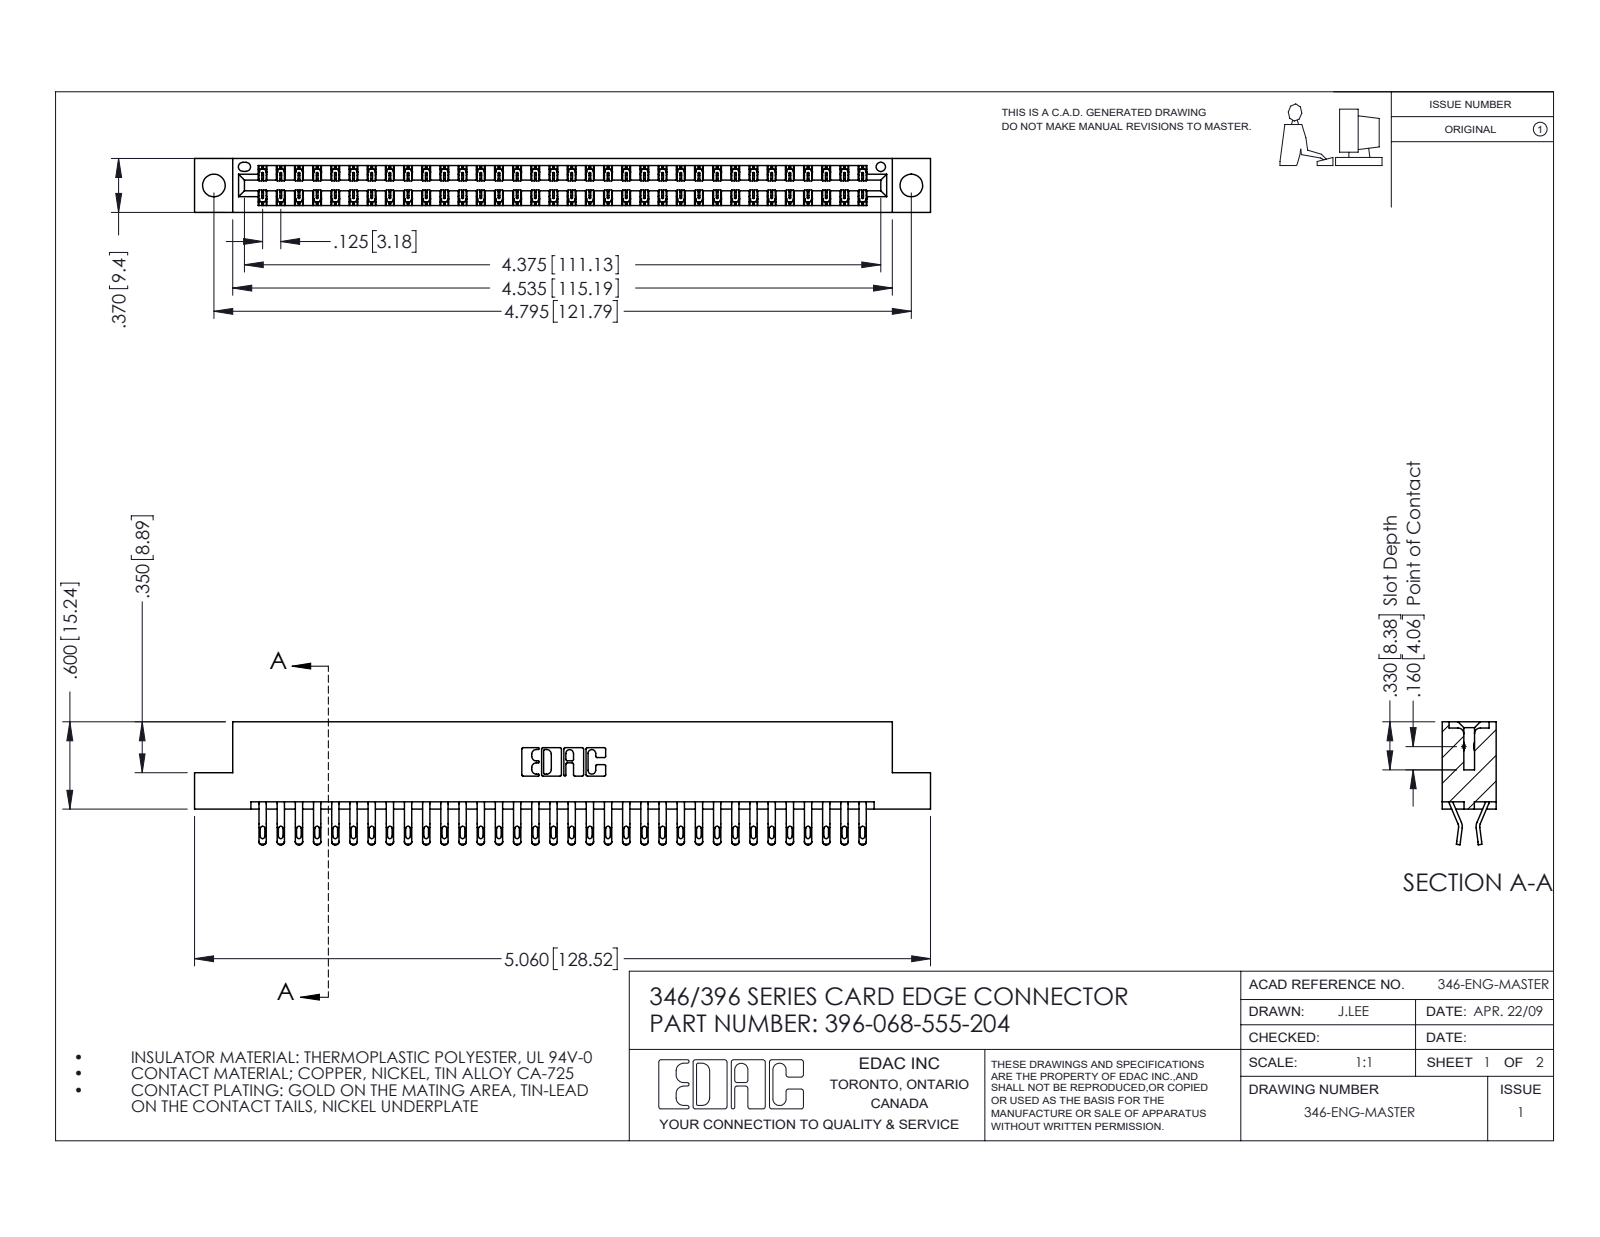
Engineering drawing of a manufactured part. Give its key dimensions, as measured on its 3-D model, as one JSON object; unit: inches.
{"part_name": "346 Part_Flush Mounting Lugs - 0.156 Dia-TH; 396-068-555-204; 345-292-001_555 Tail", "step_written_by": "SolidWorks 2016 (CONFIG_CONTROL_DESIGN)", "units": "inches", "bodies": {"solids": 69, "faces": 4066, "planar": 2320, "cylindrical": 1746, "other": 0}, "overall_size": [5.06, 0.845, 0.37], "volume_in3": 0.768, "surface_area_in2": 27.41, "round_holes": [[0.156, 2], [0.064, 1]], "partial_cylinders_radius": [[0.016, 136], [0.02, 136], [0.006, 102], [0.01, 22], [0.007, 6], [0.031, 6], [0.026, 3], [0.01, 2]], "face_to_face_distances": [0.048, 0.322, 0.37, 0.25, 0.025, 0.072, 0.298, 0.275, 0.148, 0.222], "hole_center_spacings": [0.246, 4.587, 4.795]}
